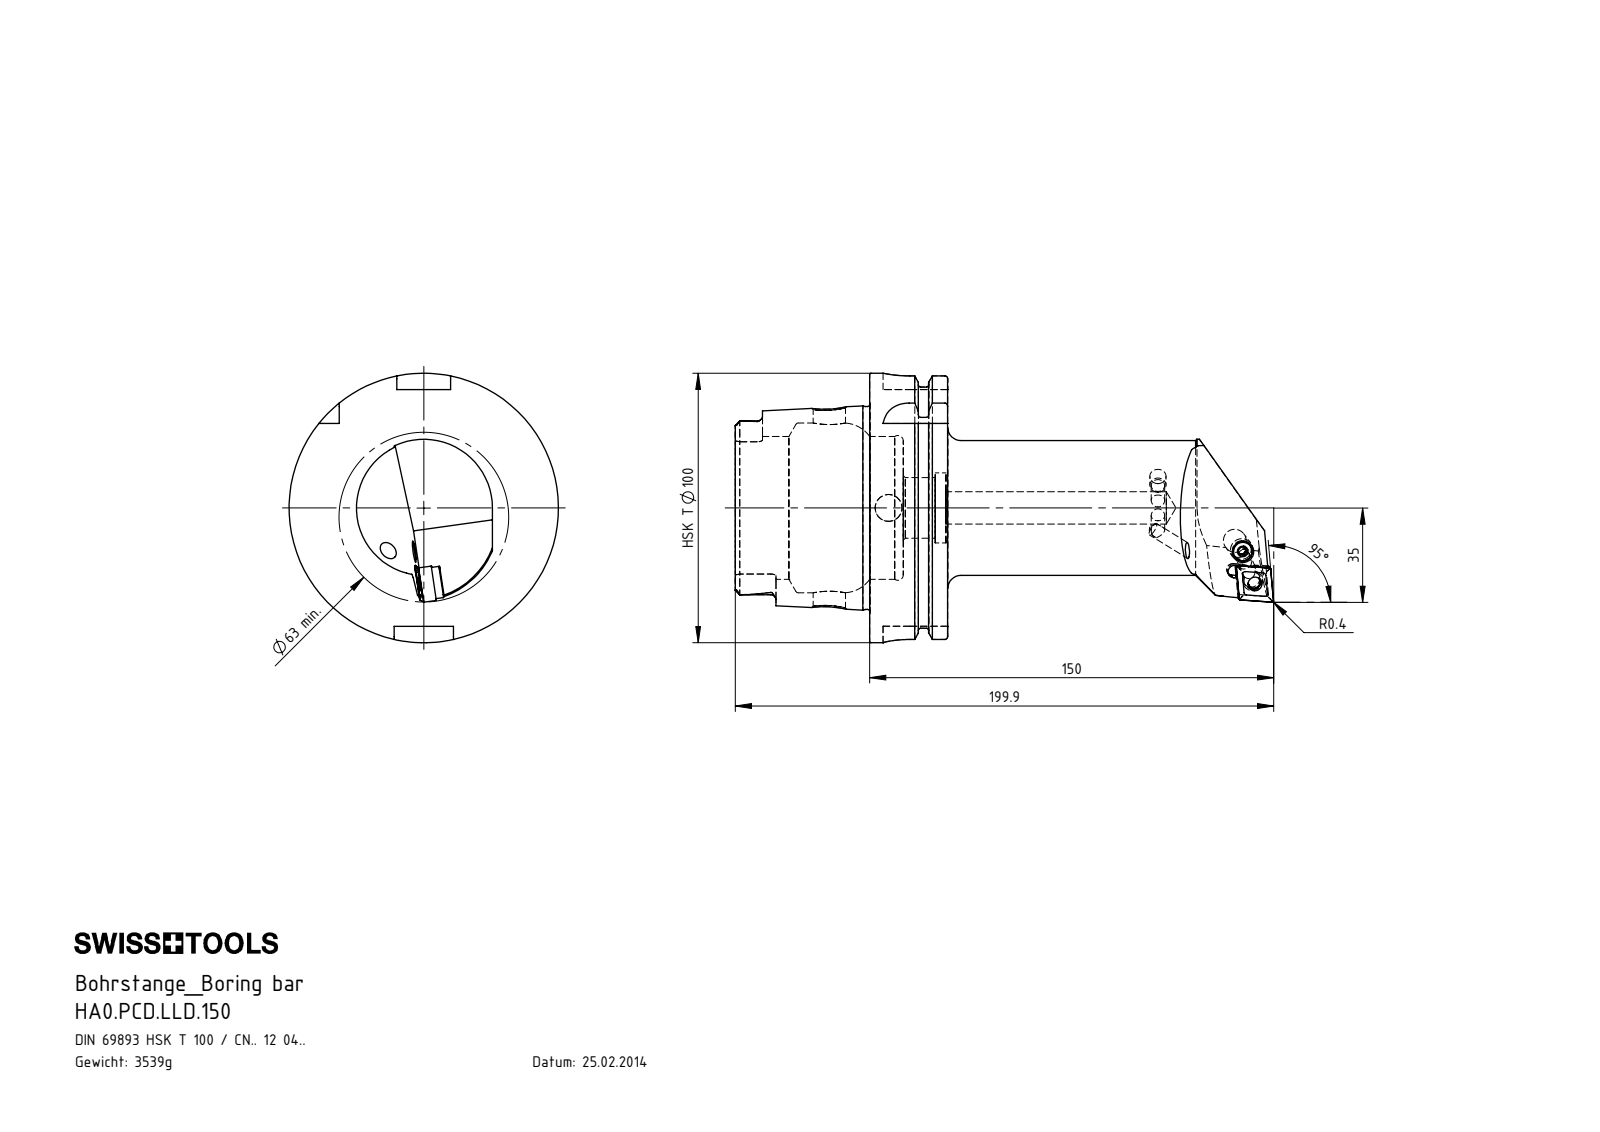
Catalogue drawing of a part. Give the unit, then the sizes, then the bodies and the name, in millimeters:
Units: millimetres
Overall size (bounding box): 199.86 × 100 × 100
Round holes (diameter × count): ⌀5 ×3, ⌀12 ×2, ⌀5.16 ×1, ⌀6 ×1, ⌀6.4 ×1, ⌀7 ×1, ⌀8.4 ×1, ⌀10 ×1, ⌀22.5 ×1, ⌀26 ×1, ⌀53 ×1, ⌀63 ×1
Round bosses / shafts (diameter × count): ⌀100 ×1, ⌀91.95 ×1, ⌀75.26 ×1, ⌀50 ×1, ⌀8 ×1, ⌀7.9 ×1, ⌀6.4 ×1, ⌀6 ×1
Partial cylindrical surfaces — rounded edges, fillets, slot ends (radius × count): R1.9 ×6, R0.4 ×4, R1 ×4, R10 ×4, R2.5 ×2, R4.83 ×2, R4.88 ×2, R2.1 ×1
Main face-to-face distances: 28.95, 12.45, 16.5, 49.9, 62.35, 78.85, 87.8, 78.2, 28.3, 15.85
Hole centre spacings: 12.81, 12.87
Volume: 449 841 mm³ · Surface area: 73 620 mm²
Bodies: 7 solids, 282 faces (111 planar, 70 cylindrical, 101 other)
Part name (STEP PRODUCT): WCD-ER4.101.017_A; HA0.PCD.LLD.150; HA0-PCD.LLD.150_A_Fertigbearbeitung; WCD-ER2.101.003_A (+3 more)
STEP written by: SolidWorks 2017 (AUTOMOTIVE_DESIGN)
